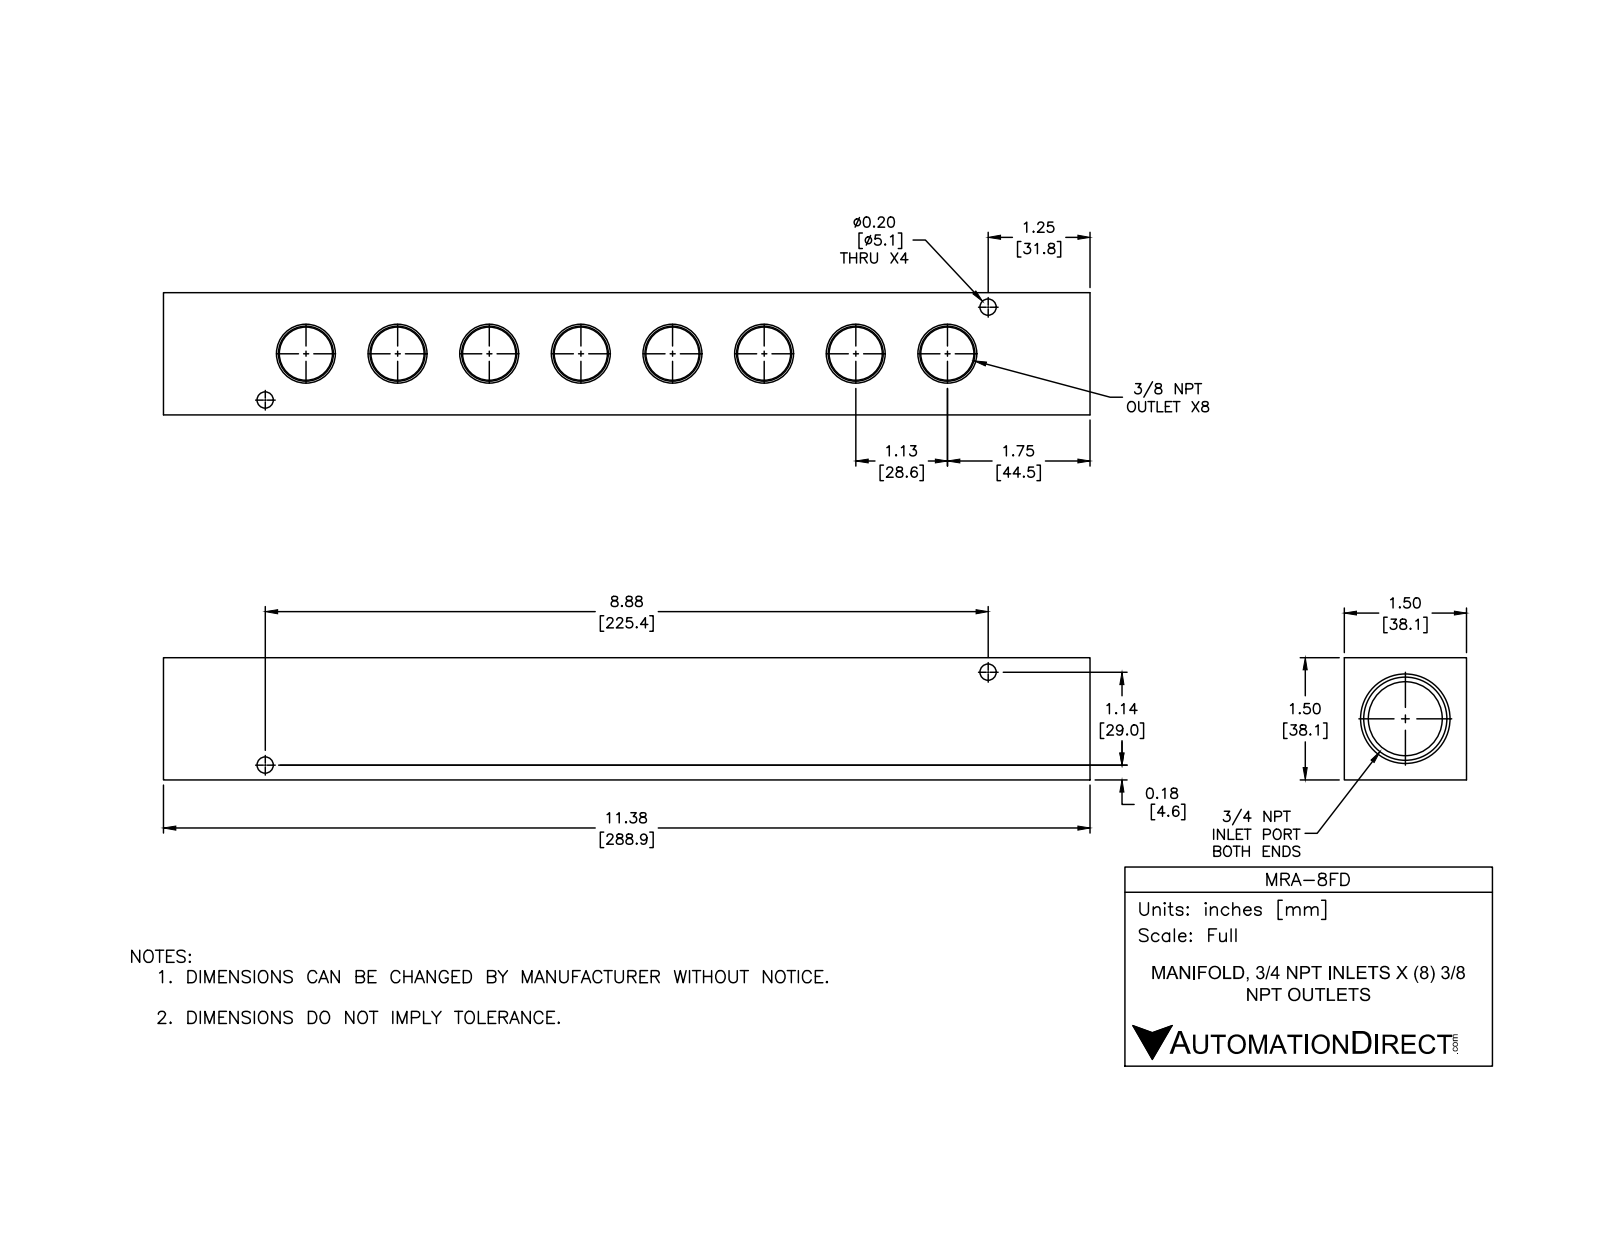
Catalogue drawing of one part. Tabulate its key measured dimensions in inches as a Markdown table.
| quantity | value |
| --- | --- |
| part name | MRA-8FD |
| STEP written by | SolidWorks 2015 (CONFIG_CONTROL_DESIGN) |
| units | inches |
| bodies | 1 solid, 82 faces (24 planar, 18 cylindrical, 40 other) |
| overall size | 11.375 × 1.5 × 1.5 |
| volume | 16.94 in³ |
| surface area | 107.4 in² |
| round holes (diameter × count) | 0.2 × 4, 0.906 × 1 |
| main face-to-face distances | 1.5, 11.375, 0.55, 10.825, 10.275, 1.09, 0.41 |
| hole center spacings | 8.948 |
